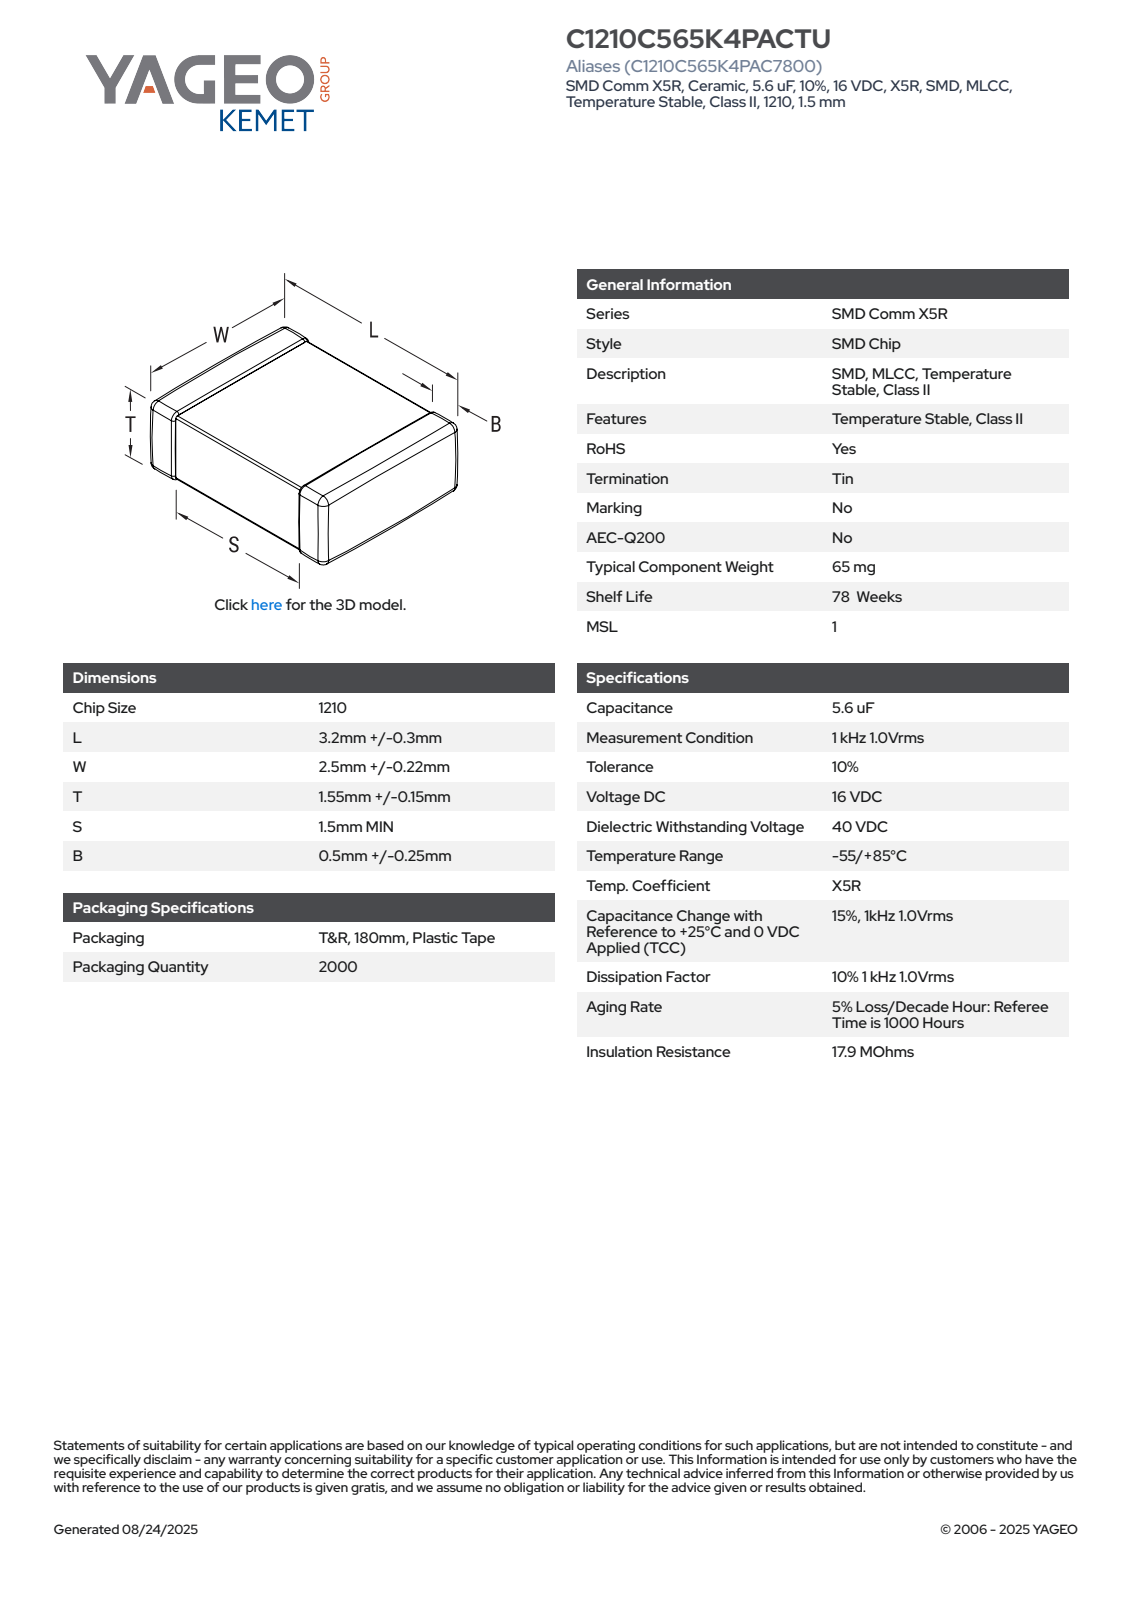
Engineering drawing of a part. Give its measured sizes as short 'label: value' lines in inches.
name: CCS_CCSTD_1210_L3.5W2.72T1.7B0.5
written by: SolidWorks 2021 (AUTOMOTIVE_DESIGN)
unit: in
bodies: 4 solids, 125 faces (71 planar, 38 cylindrical, 16 other)
size: 0.138 × 0.107 × 0.067
volume: 0.001 in³; area: 0.062 in²
face distances: 0.065, 0.062, 0.138, 0.105, 0.067, 0.102, 0.107, 0.065, 0.063, 0.059
